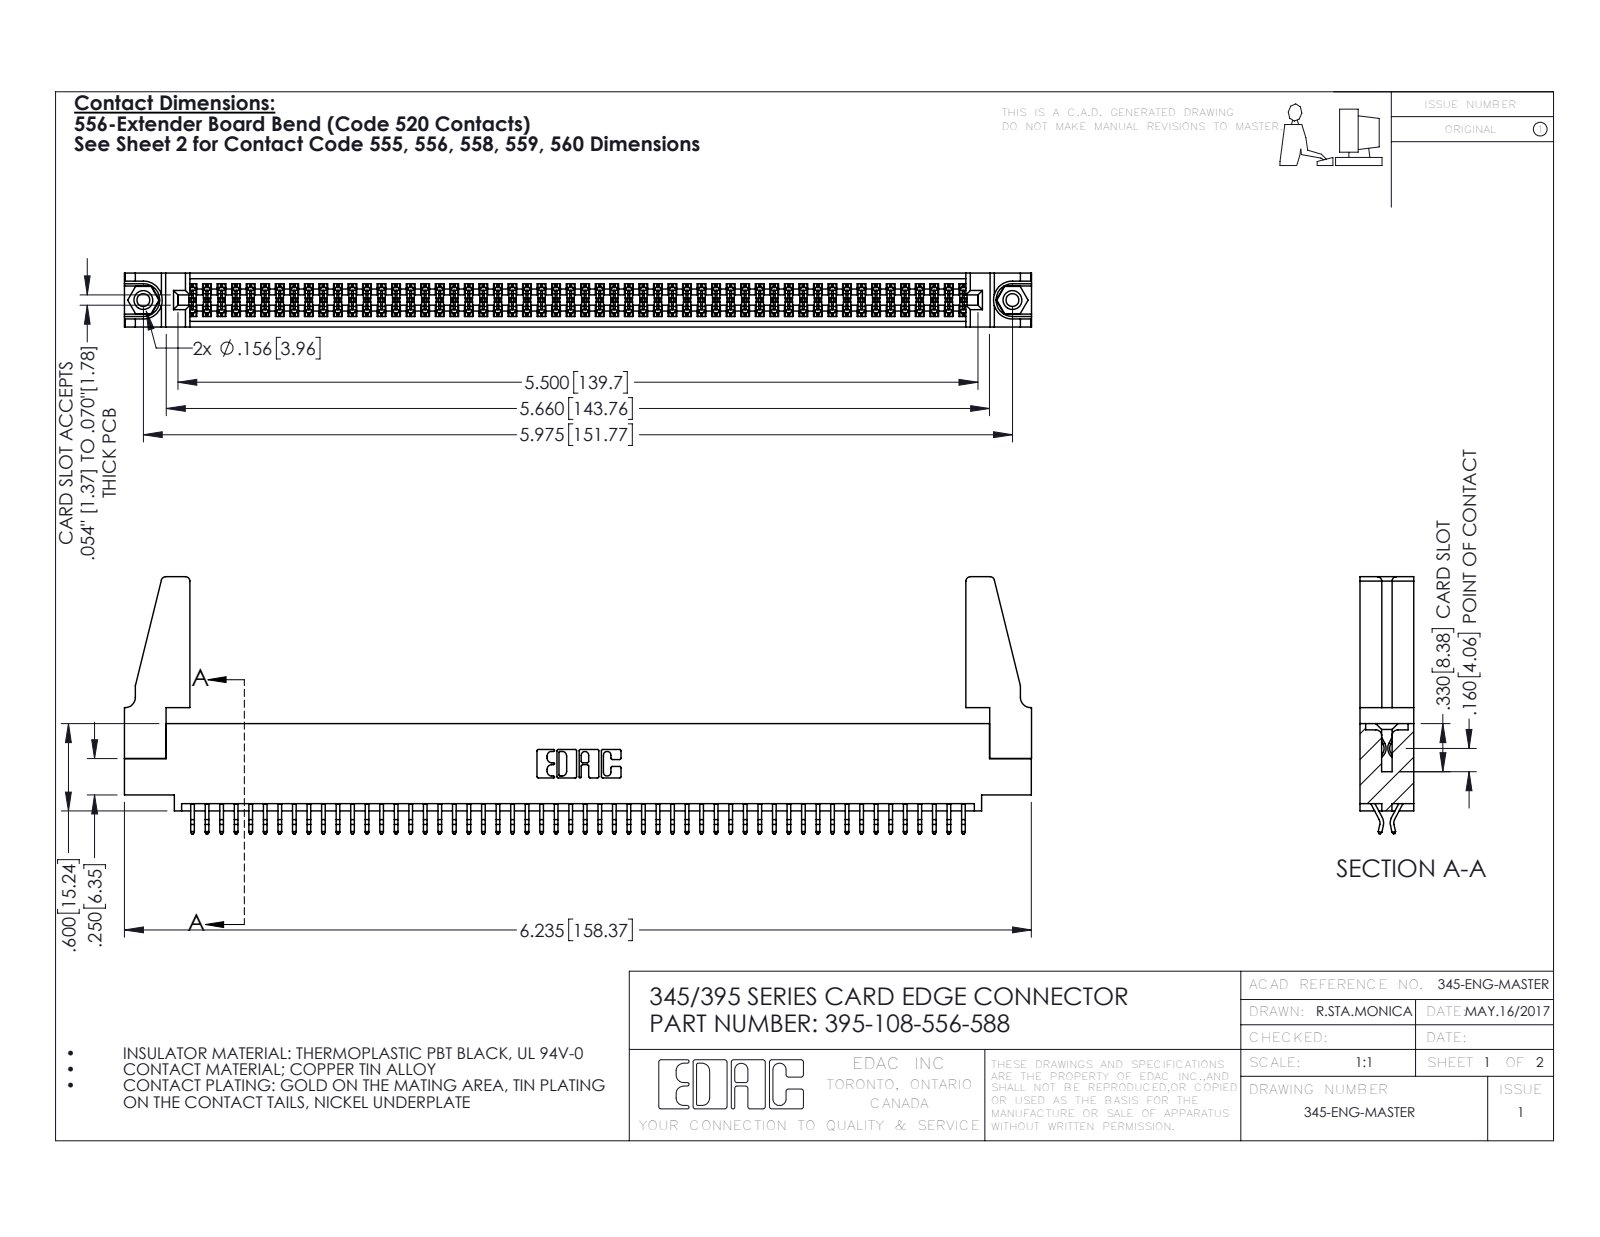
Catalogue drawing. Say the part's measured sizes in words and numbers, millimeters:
The part is named "345-292-001_556 Tail; 345-250-001_345-250-001-102; 345 Part_0.110 Offset - 0.156 Dia-TH; 395-108-556-588 (+1 more)". Its 3-D file was written by "SolidWorks 2016 (CONFIG_CONTROL_DESIGN)". It is 113 solids with 6302 faces: 4152 planar, 2134 cylindrical and 16 other. Overall it measures 158.4 by 44.9 by 9.4 millimeters. Its volume is 18 660 cubic millimeters and its surface area 26 150 square millimeters. Round holes: 2 of diameter 2.3, 2 of diameter 3.2, 2 of diameter 4, 1 of diameter 1.6. Round bosses or shafts: 2 of diameter 3.9. Partial cylindrical surfaces (rounded edges, fillets, slot ends): 162 of radius 0.2, 22 of radius 0.3, 8 of radius 0.8, 6 of radius 0.2, 6 of radius 0.8, 3 of radius 0.7, 2 of radius 0.3, 2 of radius 0.4. The main face-to-face distances are 1.8, 7.6, 9.4, 0.6, 5.1, 2.5, 6.9, 5.7, 4.4, 3.8. The hole center spacings are 6.9, 145.8, 151.8.
